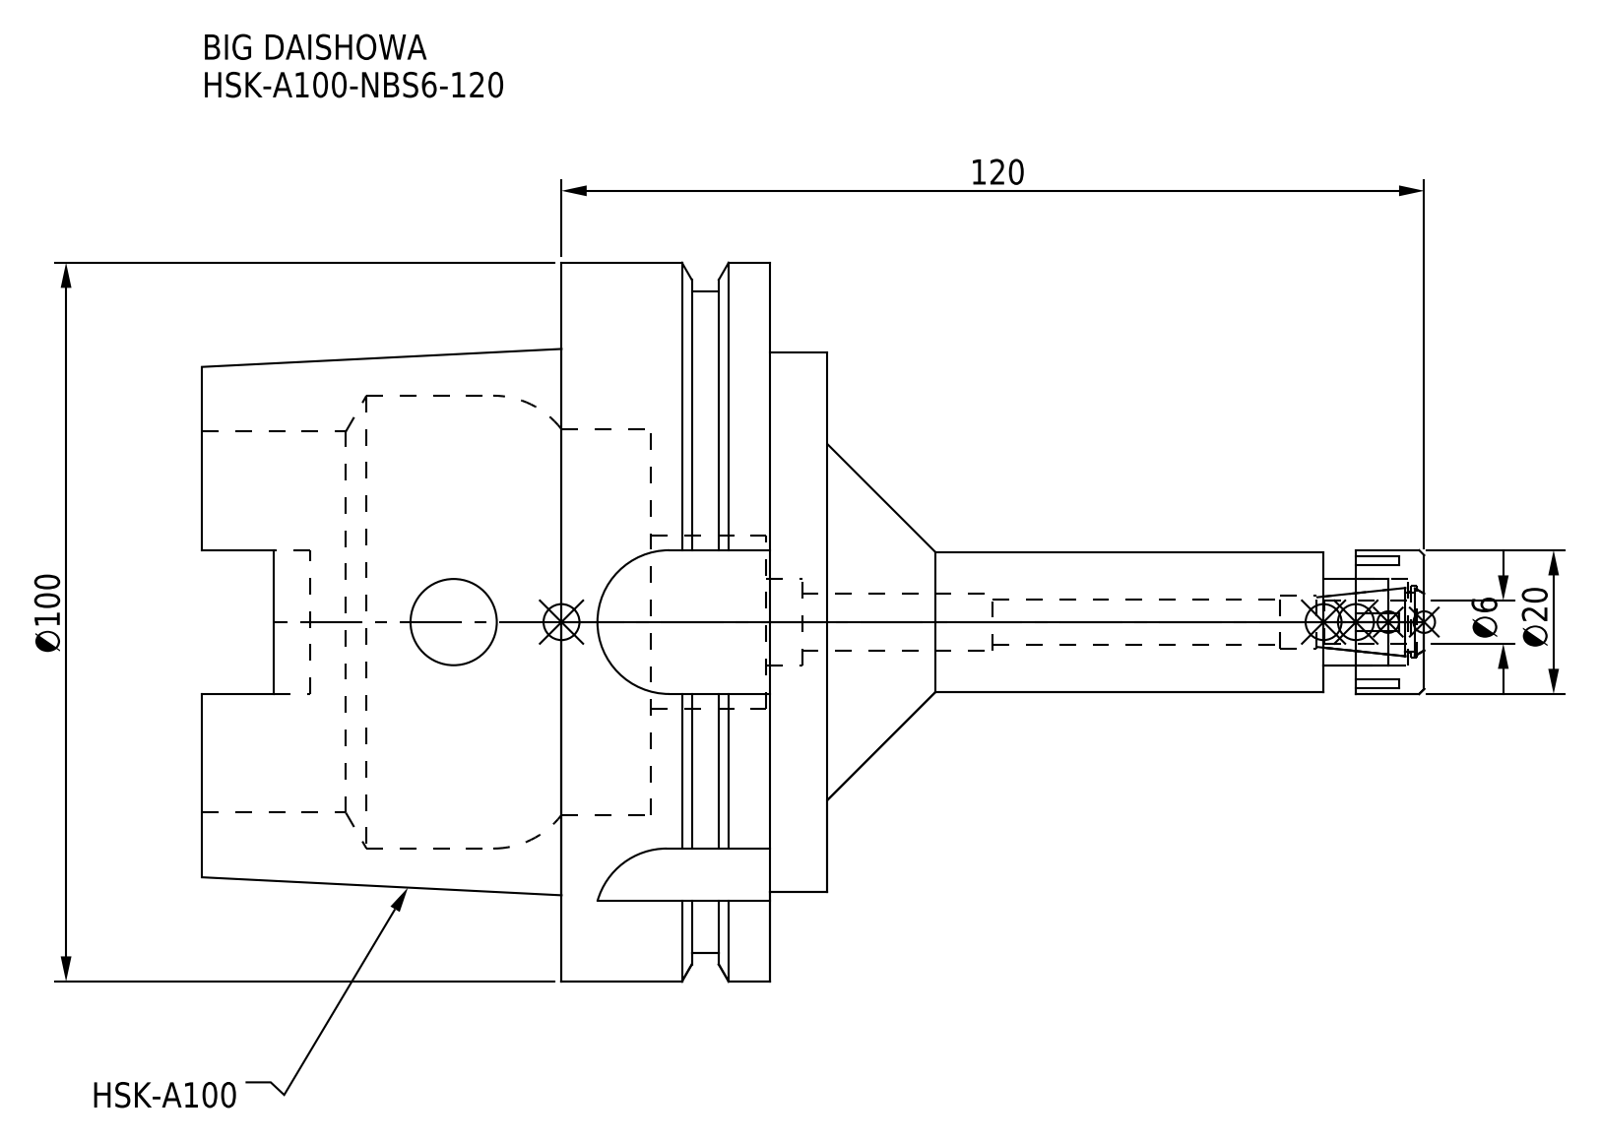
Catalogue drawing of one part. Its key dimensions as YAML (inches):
part_name: "HSK-A100-NBS6-120.stp; HSK-A100-NBS6-120-FreeParts; HA100NB06120-060_ASM.stp; HSK-A100-NBS6-120 (+3 more)"
step_written_by: "SolidWorks 2019 (CONFIG_CONTROL_DESIGN)"
units: inches
bodies: {solids: 2, faces: 141, planar: 67, cylindrical: 52, other: 22}
overall_size: [6.693, 3.937, 3.937]
volume: 19.47
surface_area: 92.58
round_holes:
  - {diameter: 0.472, count: 2}
  - {diameter: 0.252, count: 1}
  - {diameter: 0.295, count: 1}
  - {diameter: 0.315, count: 1}
  - {diameter: 0.335, count: 1}
  - {diameter: 0.394, count: 1}
  - {diameter: 0.945, count: 1}
  - {diameter: 2.087, count: 1}
  - {diameter: 2.118, count: 1}
  - {diameter: 2.48, count: 1}
round_bosses_or_shafts:
  - {diameter: 3.937, count: 1}
  - {diameter: 3.622, count: 1}
  - {diameter: 2.953, count: 1}
  - {diameter: 0.787, count: 1}
  - {diameter: 0.768, count: 1}
partial_cylinders:
  - {radius: 0.192, count: 4}
  - {radius: 0.394, count: 4}
face_to_face_distances: [1.142, 0.315, 1.457, 0.967, 0.652, 0.49, 3.425, 3.11, 2.459, 1.969]
